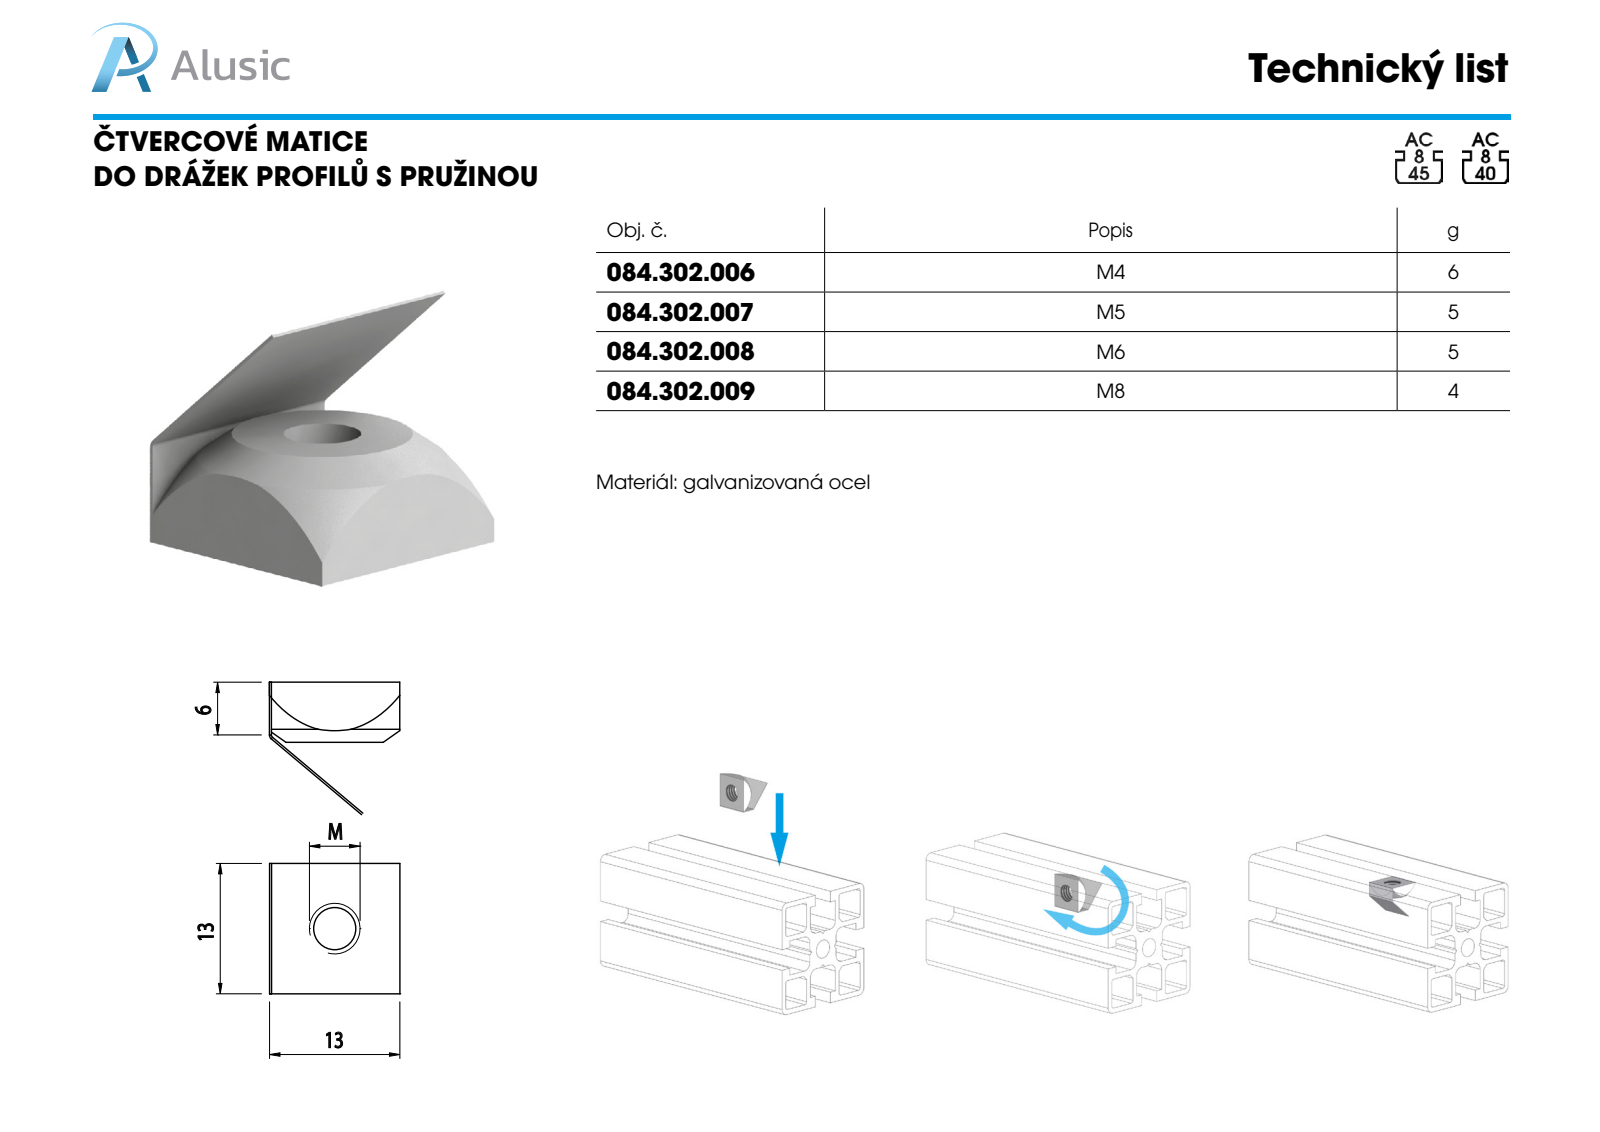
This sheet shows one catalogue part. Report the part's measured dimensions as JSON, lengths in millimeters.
{"part_name": "084.302.008", "step_written_by": "SolidWorks 2012 (CONFIG_CONTROL_DESIGN)", "units": "millimeters", "bodies": {"solids": 2, "faces": 28, "planar": 18, "cylindrical": 4, "other": 6}, "overall_size": [13.21, 13, 13], "volume_mm3": 866, "surface_area_mm2": 1080, "round_holes": [[4.2, 1]], "partial_cylinders_radius": [[0.3, 1], [0.5, 1]], "face_to_face_distances": [13, 6, 12.8]}
